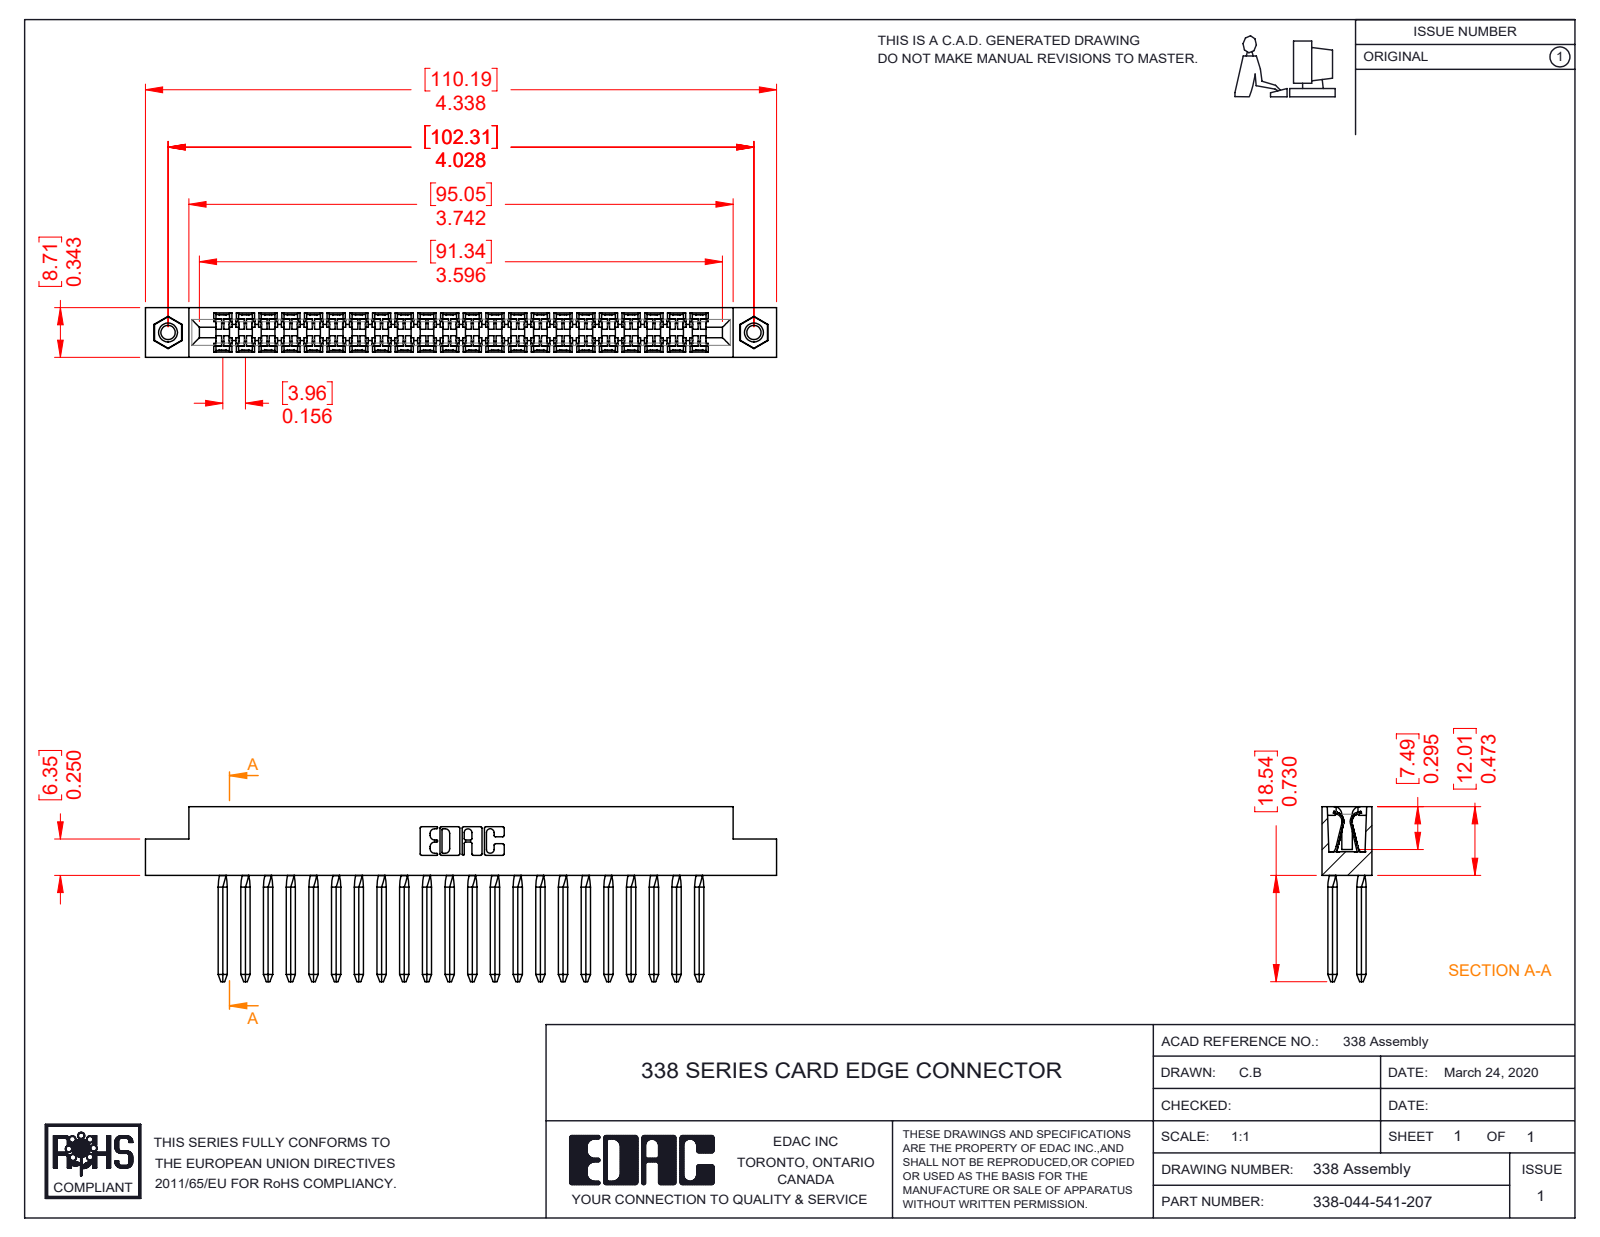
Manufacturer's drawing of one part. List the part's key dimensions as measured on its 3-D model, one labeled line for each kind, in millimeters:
Part name (STEP PRODUCT): 338-210-001_338-210-022-004; 338-044-541-207; 345-250-001_345-250-005-103; 338-290-001_541
STEP written by: SolidWorks 2016 (CONFIG_CONTROL_DESIGN)
Units: millimetres
Bodies: 47 solids, 3102 faces (2150 planar, 760 cylindrical, 192 other)
Overall size (bounding box): 110.2 × 30.6 × 8.7
Volume: 8 460 mm³ · Surface area: 15 670 mm²
Round holes (diameter × count): ⌀2.5 ×2, ⌀3.2 ×2, ⌀4 ×2
Round bosses / shafts (diameter × count): ⌀3.9 ×2
Partial cylindrical surfaces — rounded edges, fillets, slot ends (radius × count): R0.6 ×134, R0.2 ×44, R1.4 ×36, R1.7 ×36, R2.5 ×35, R0.3 ×22, R0.2 ×6, R0.8 ×6
Main face-to-face distances: 8.7, 4, 2.8, 15.8, 5.3, 3.4, 19.8, 11.9, 5.6, 11.2
Hole centre spacings: 102.3
